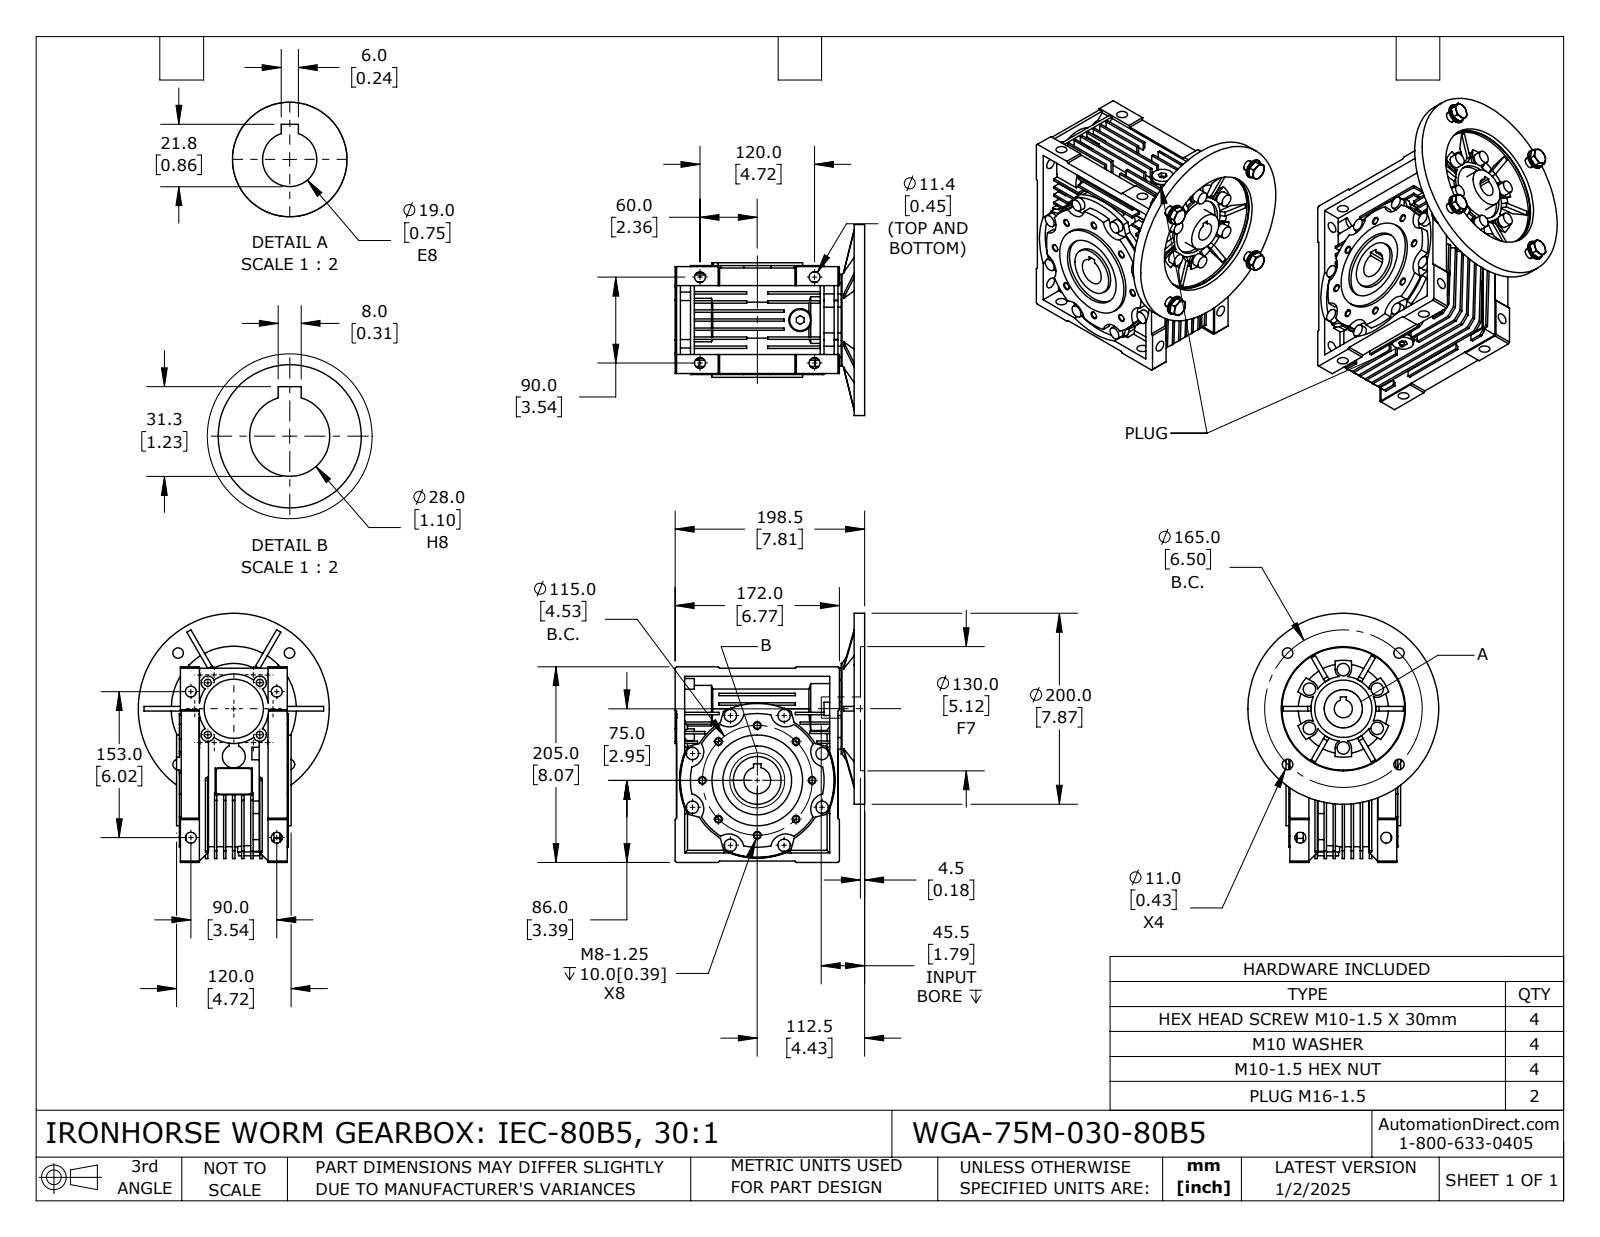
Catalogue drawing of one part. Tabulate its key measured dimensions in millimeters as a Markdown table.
| quantity | value |
| --- | --- |
| part name | WGA-75M-030-80B5 |
| STEP written by | SolidWorks 2024 (CONFIG_CONTROL_DESIGN) |
| units | millimeters |
| bodies | 8 solids, 1203 faces (690 planar, 391 cylindrical, 122 other) |
| overall size | 261 × 200 × 198.5 |
| volume | 3 029 000 mm³ |
| surface area | 523 078 mm² |
| round holes (diameter × count) | 6.65 × 8, 11.38 × 8, 7.45 × 4, 11 × 4, 14.5 × 2, 19 × 1, 20 × 1, 28 × 1, 39 × 1, 42 × 1, 50 × 1, 62 × 1 |
| round bosses / shafts (diameter × count) | 13 × 14, 24 × 3, 95 × 2, 22 × 2, 15.8 × 2, 13.7 × 2, 200 × 1, 139.93 × 1 |
| partial cylindrical surfaces (radius × count) | 7 × 10, 16 × 8, 8.5 × 6, 2.5 × 4, 33.99 × 1, 36 × 1, 36.5 × 1, 39 × 1 |
| main face-to-face distances | 9.5, 2.5, 19, 12, 7, 28.5, 16.5, 10, 27.75, 4 |
| hole center spacings | 44.01, 57.5, 81.32, 91.04, 106.25, 38.49, 54.44, 82.51 |
